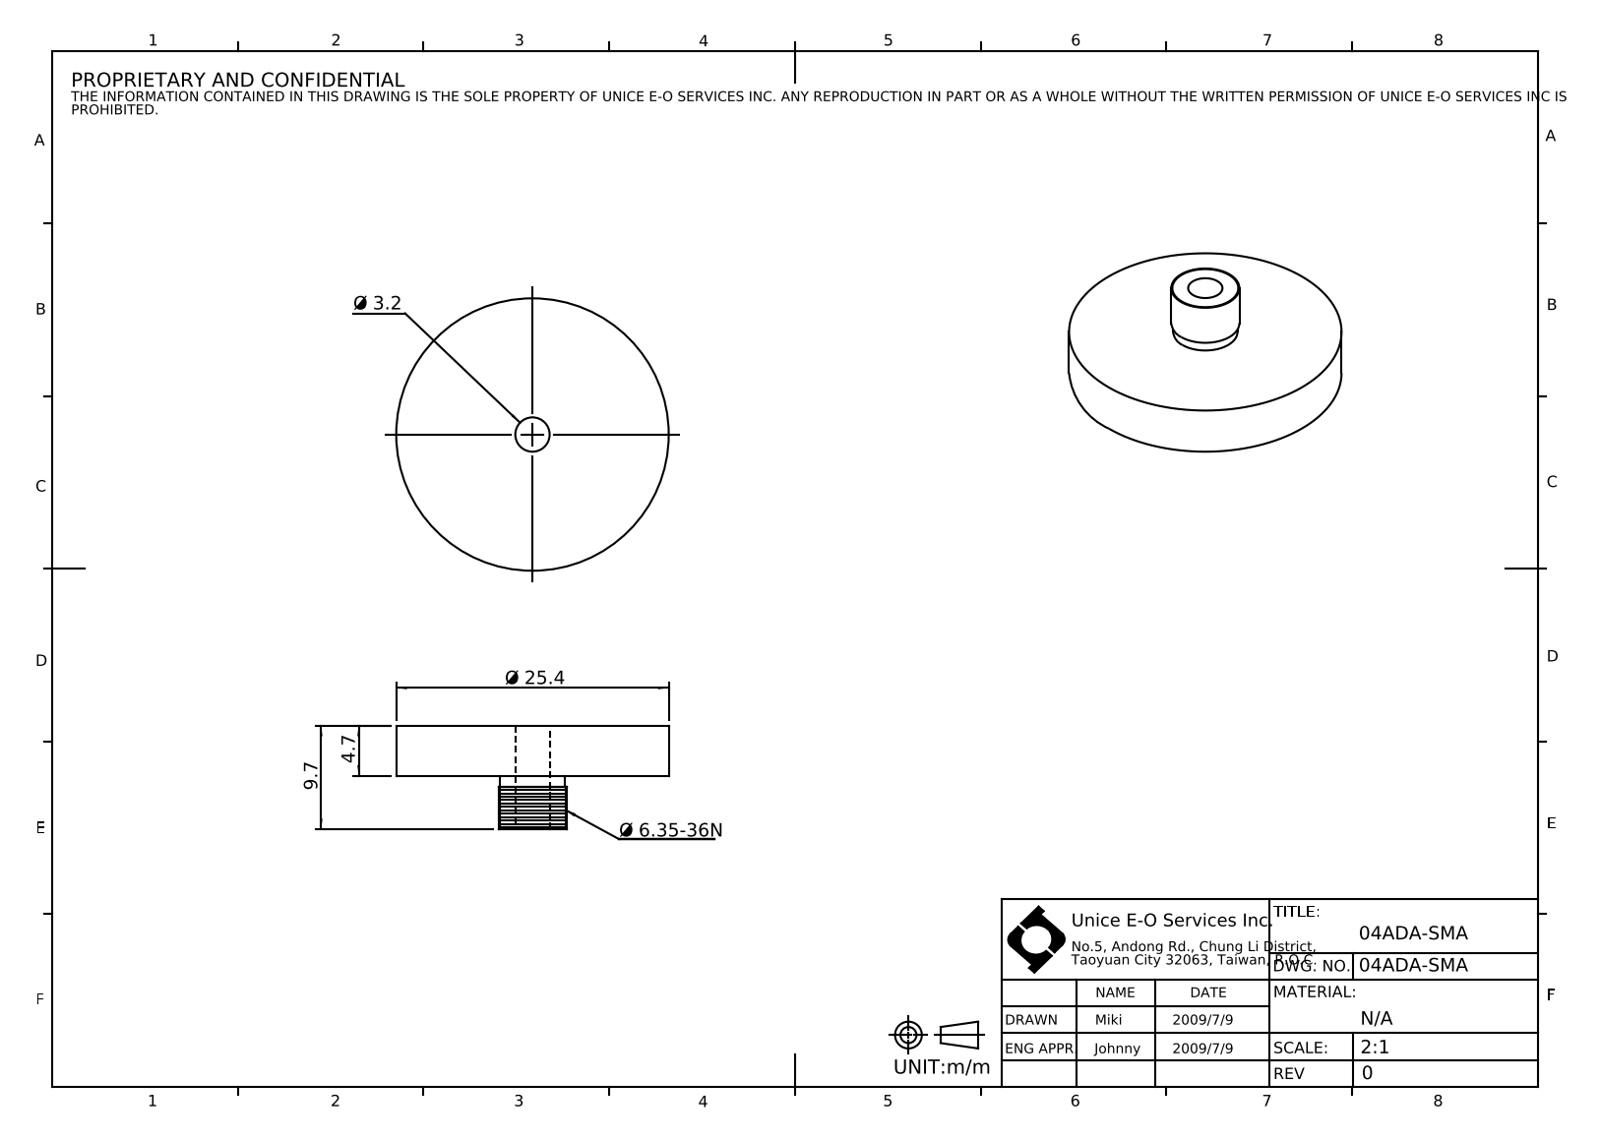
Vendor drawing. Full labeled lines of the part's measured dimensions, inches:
Part name (STEP PRODUCT): 04ADA-SMA
STEP written by: SolidWorks 2016 (CONFIG_CONTROL_DESIGN)
Units: inches
Bodies: 1 solid, 12 faces (4 planar, 8 cylindrical, 0 other)
Overall size (bounding box): 1 × 1 × 0.382
Volume: 0.15 in³ · Surface area: 2.441 in²
Round holes (diameter × count): ⌀0.126 ×1
Round bosses / shafts (diameter × count): ⌀1 ×1, ⌀0.25 ×1, ⌀0.236 ×1
Main face-to-face distances: 0.185, 0.382, 0.197, 0.224, 0.039, 0.157
